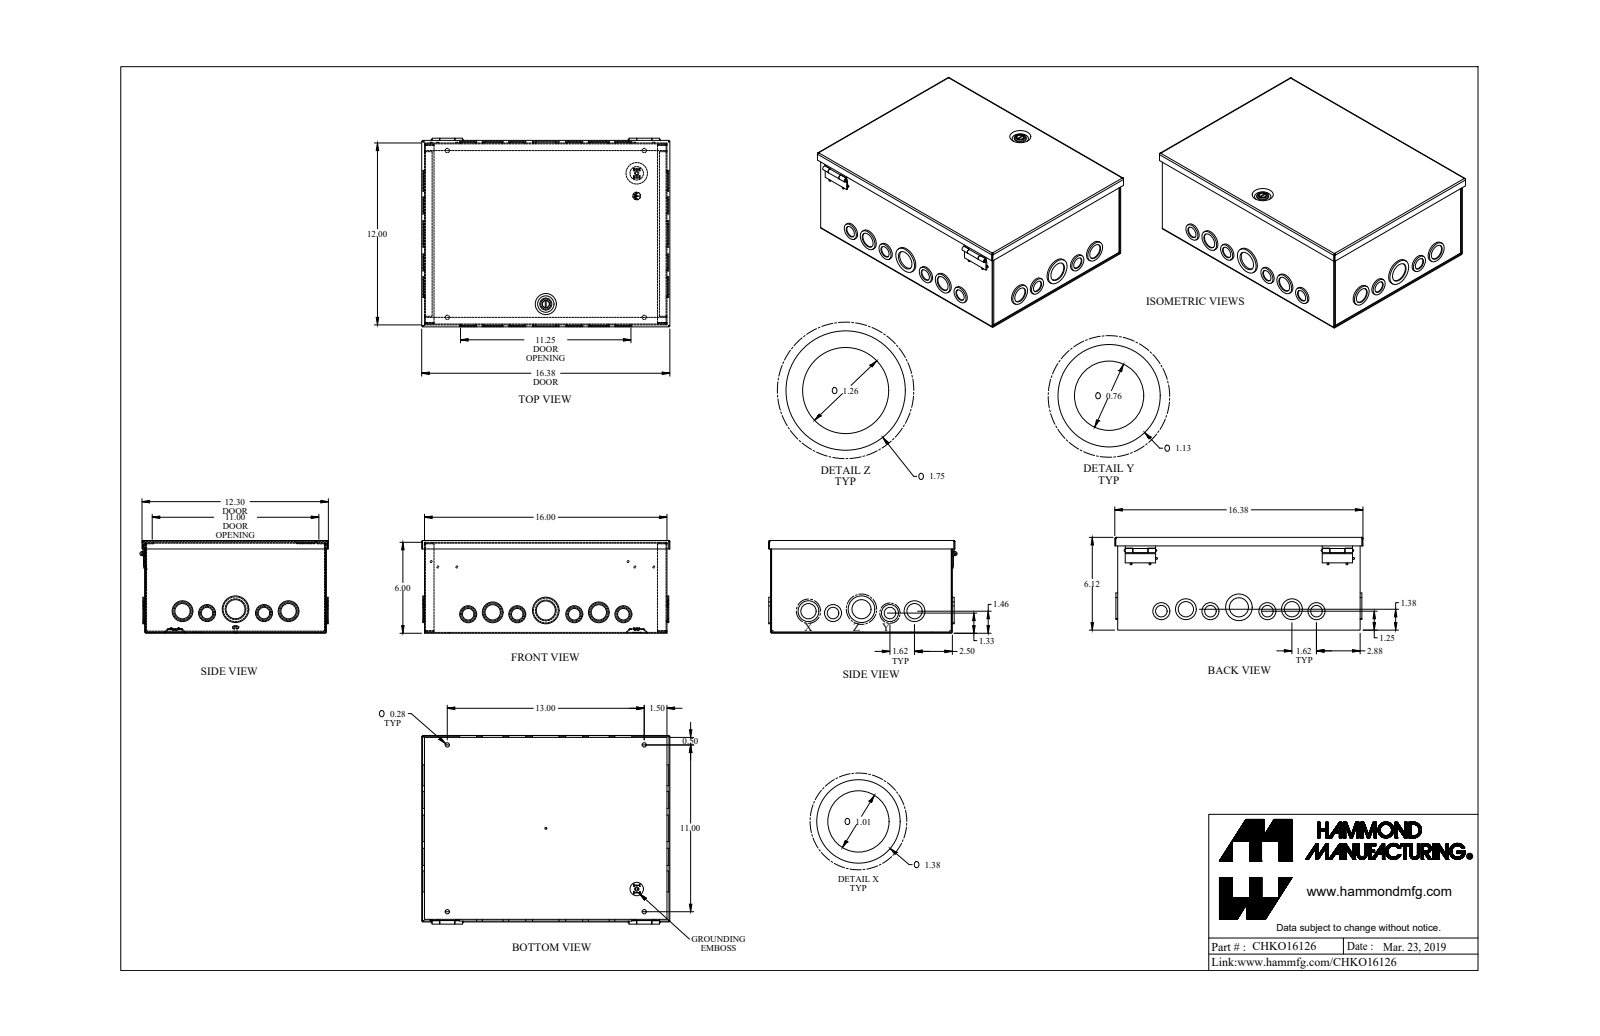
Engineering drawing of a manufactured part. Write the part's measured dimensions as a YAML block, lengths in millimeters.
part_name: "CHKO16126_Default"
step_written_by: "SolidWorks 2019 (CONFIG_CONTROL_DESIGN)"
units: millimeters
bodies: {solids: 12, faces: 775, planar: 368, cylindrical: 364, other: 43}
overall_size: [416.1, 316.1, 155.4]
volume: 776400
surface_area: 1077000
round_holes:
  - {diameter: 25.7, count: 10}
  - {diameter: 19.3, count: 6}
  - {diameter: 32, count: 6}
  - {diameter: 7.1, count: 4}
  - {diameter: 41.6, count: 2}
  - {diameter: 3.2, count: 1}
  - {diameter: 4.3, count: 1}
  - {diameter: 8.1, count: 1}
  - {diameter: 12.1, count: 1}
  - {diameter: 12.7, count: 1}
round_bosses_or_shafts:
  - {diameter: 28.6, count: 8}
  - {diameter: 3.3, count: 8}
  - {diameter: 22.2, count: 6}
  - {diameter: 22.2, count: 6}
  - {diameter: 34.9, count: 5}
  - {diameter: 34.9, count: 3}
  - {diameter: 44.5, count: 2}
  - {diameter: 28.6, count: 2}
partial_cylinders:
  - {radius: 0.7, count: 16}
  - {radius: 2.2, count: 16}
  - {radius: 1.4, count: 8}
  - {radius: 0.3, count: 4}
  - {radius: 2.5, count: 4}
  - {radius: 0.9, count: 2}
  - {radius: 2, count: 2}
  - {radius: 6.4, count: 2}
face_to_face_distances: [1.4, 153.9, 155.4, 152.5, 303.4, 405, 304.8, 301.9, 406.4, 403.5]
hole_center_spacings: [41.3, 48.2, 89, 136.7, 177.8, 82.3, 95.5, 130.2]
